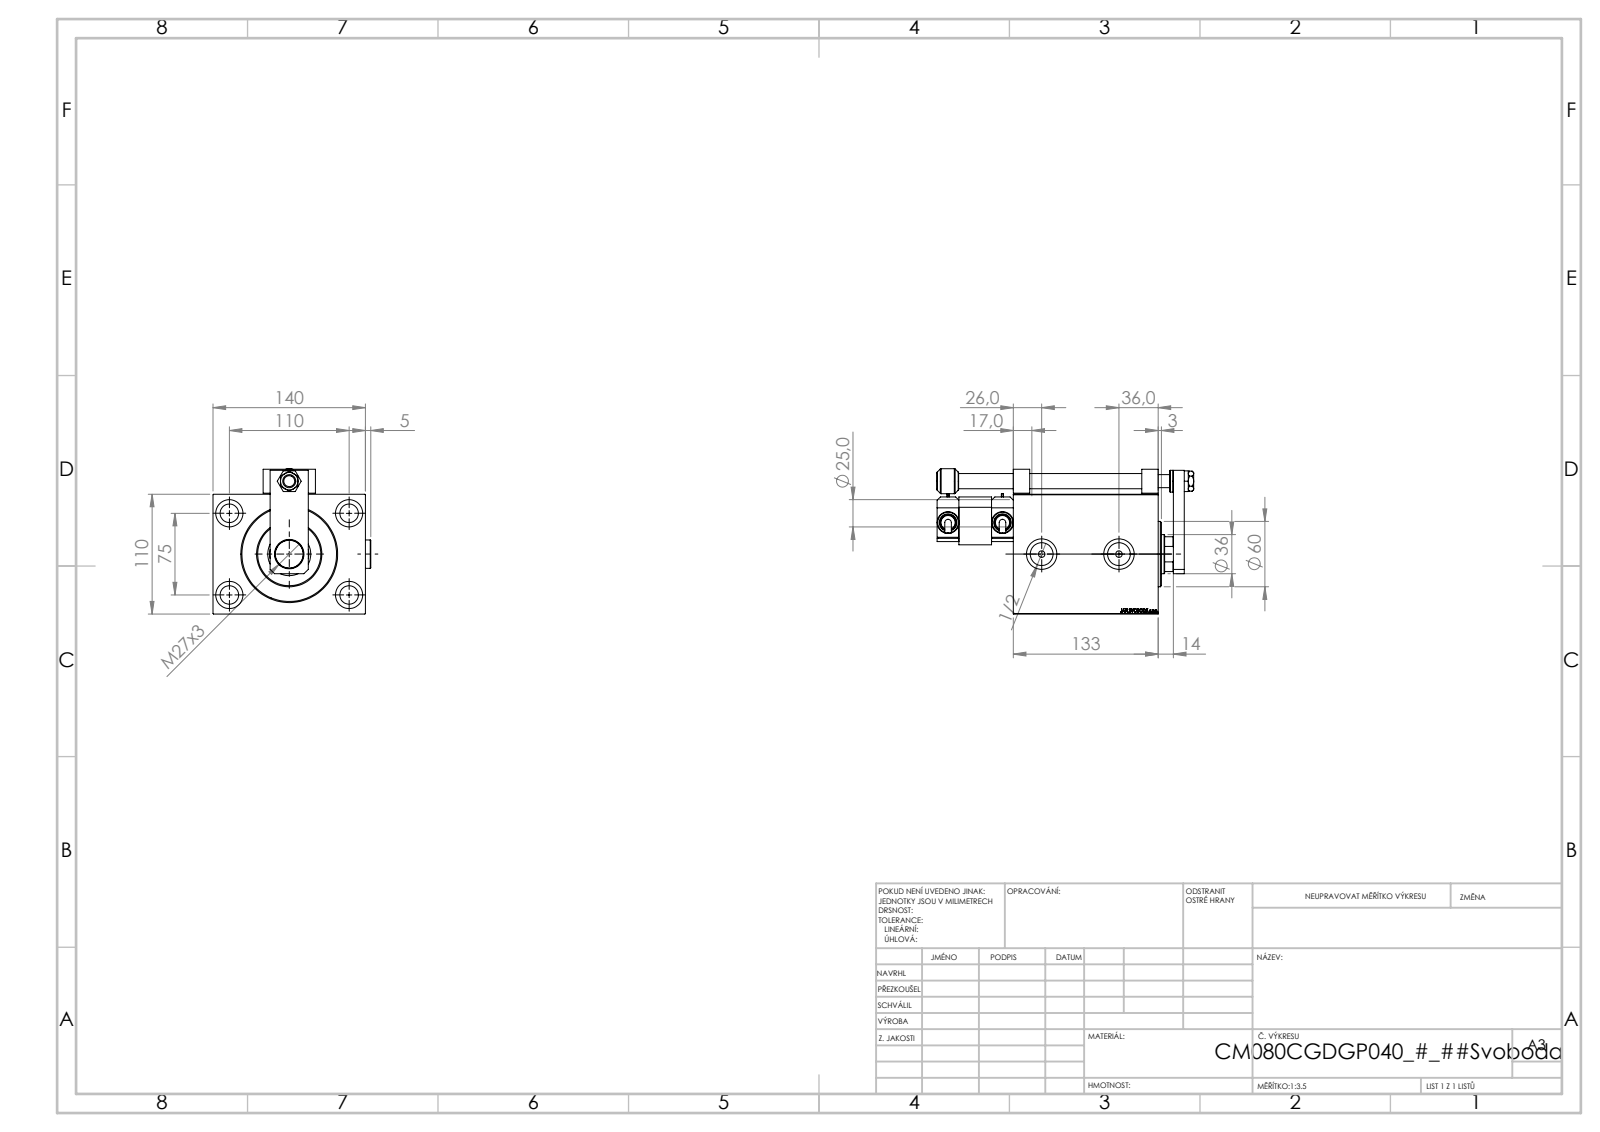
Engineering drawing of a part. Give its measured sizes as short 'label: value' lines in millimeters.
name: SWITCH P; V450CM_VC_B; TYC_P; V450CM_C_Body (+7 more)
written by: SolidWorks 2019 (CONFIG_CONTROL_DESIGN)
unit: mm
bodies: 16 solids, 1144 faces (555 planar, 136 cylindrical, 453 other)
size: 236 × 144.9 × 133.5
volume: 1 924 000 mm³; area: 269 861 mm²
holes: 4× ⌀4, 4× ⌀8, 4× ⌀17, 4× ⌀25, 2× ⌀6, 2× ⌀20.96, 2× ⌀28, 1× ⌀12, 1× ⌀13, 1× ⌀14, 1× ⌀25.5, 1× ⌀27
bosses: 3× ⌀20, 2× ⌀26, 2× ⌀16, 2× ⌀14, 2× ⌀6, 1× ⌀60, 1× ⌀23
rounds: 1× R3, 1× R17.5
face distances: 110, 140, 133, 21, 112, 50, 14, 40, 20, 119
hole spacings: 66.57, 20, 62.41, 75, 110, 118, 118.09, 119.68
